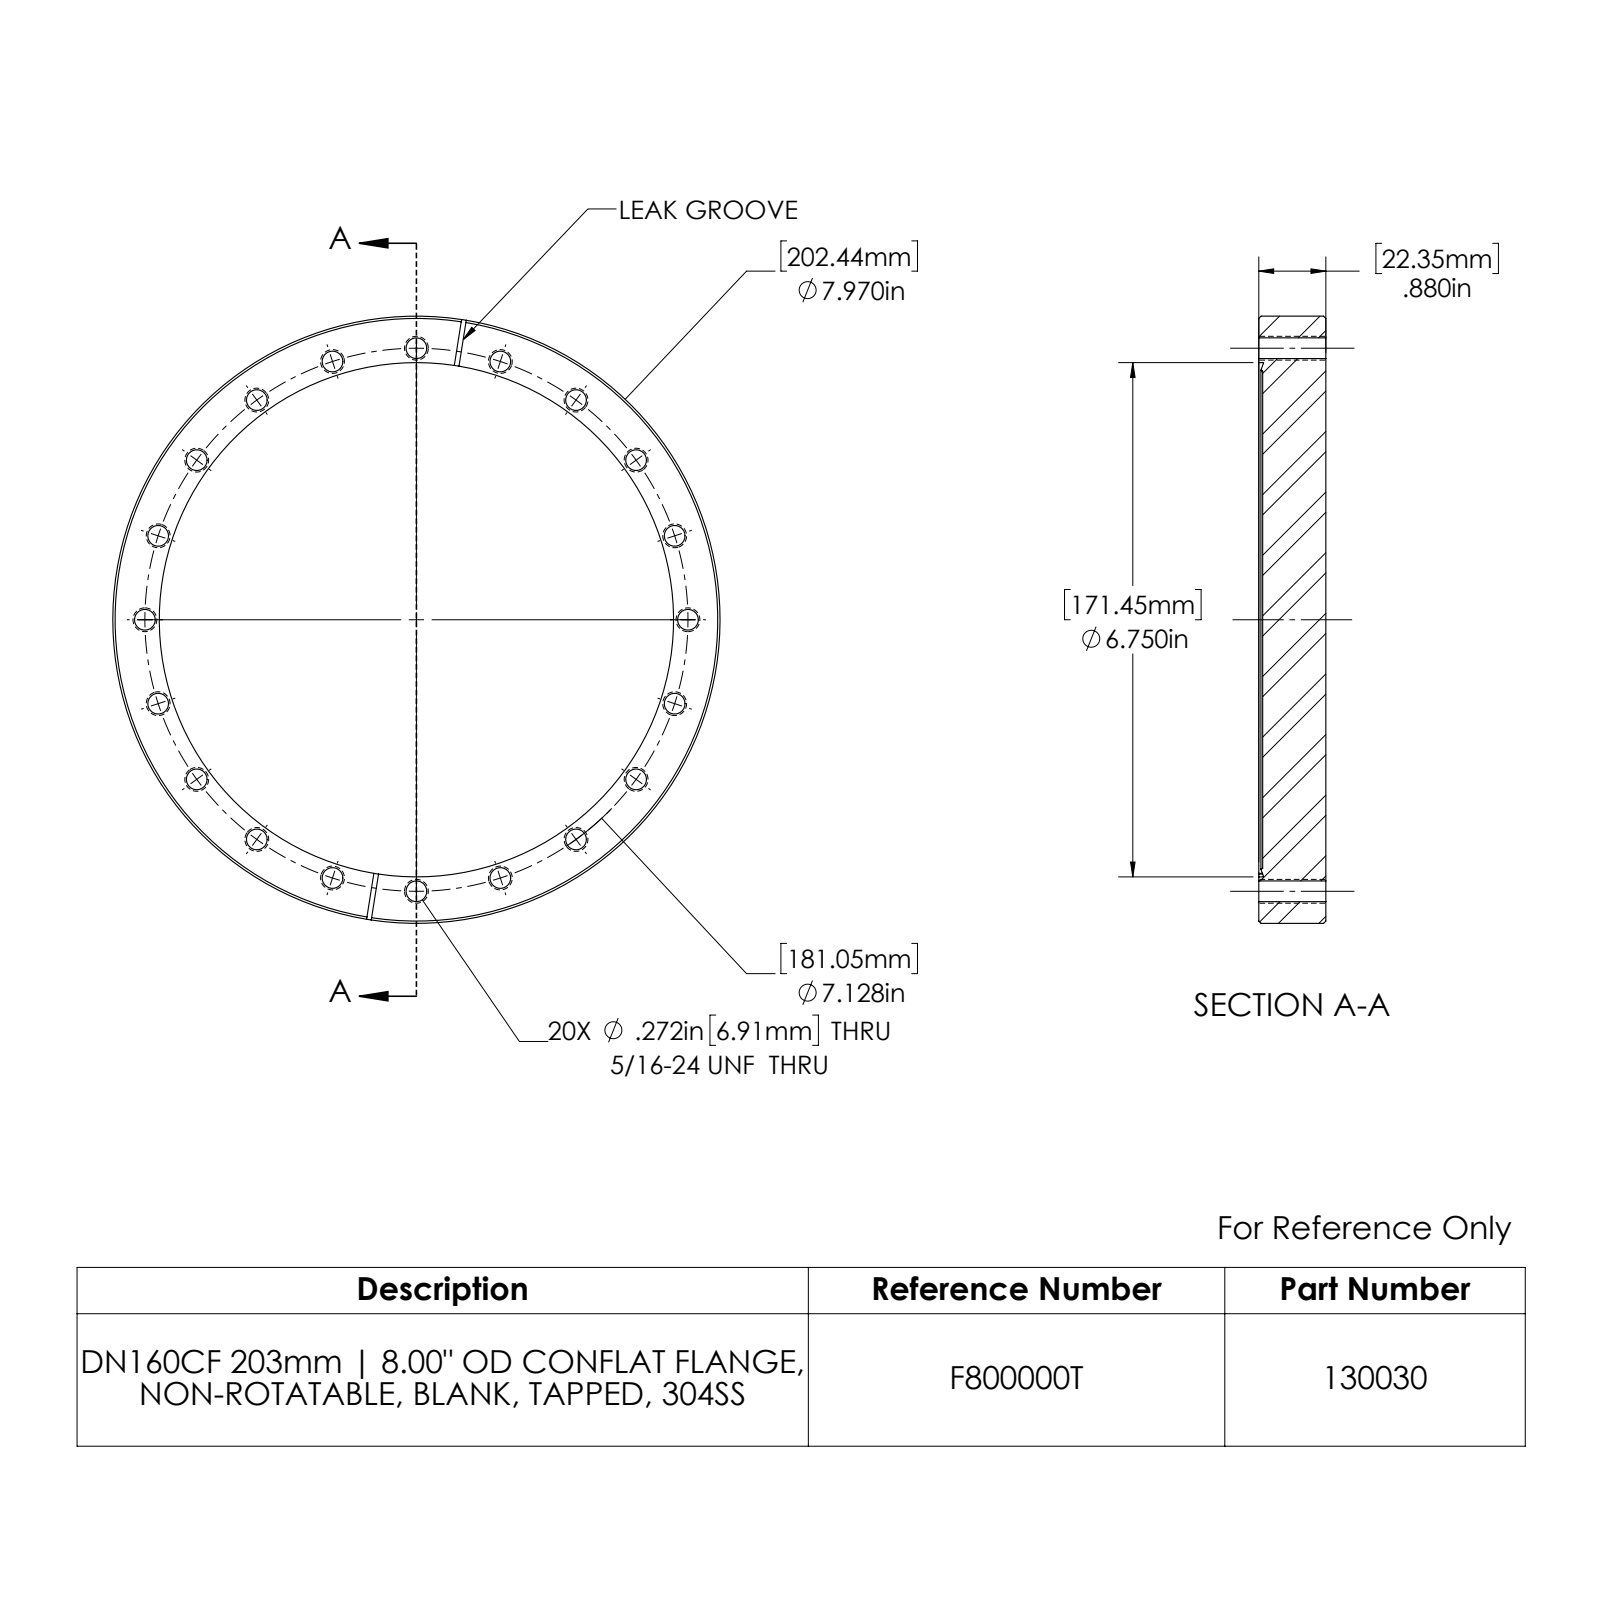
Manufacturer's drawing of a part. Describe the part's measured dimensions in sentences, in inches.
The part is named "130030". Its 3-D file was written by "SolidWorks 2022 (AUTOMOTIVE_DESIGN)". It is 1 solid with 69 faces: 10 planar, 44 cylindrical and 15 other. Overall it measures 7.97 by 7.97 by 0.88 inches. Its volume is 41.04 cubic inches and its surface area 135.5 square inches. Round holes: 20 of diameter 0.272, 1 of diameter 6.75. Round bosses or shafts: 1 of diameter 7.97. The main face-to-face distances are 0.829, 0.051, 0.88, 0.052, 0.828, 0.062, 0.066, 0.059. The hole center spacings are 4.19, 1.115, 2.203, 5.767, 6.351, 7.04, 3.236, 3.564.
